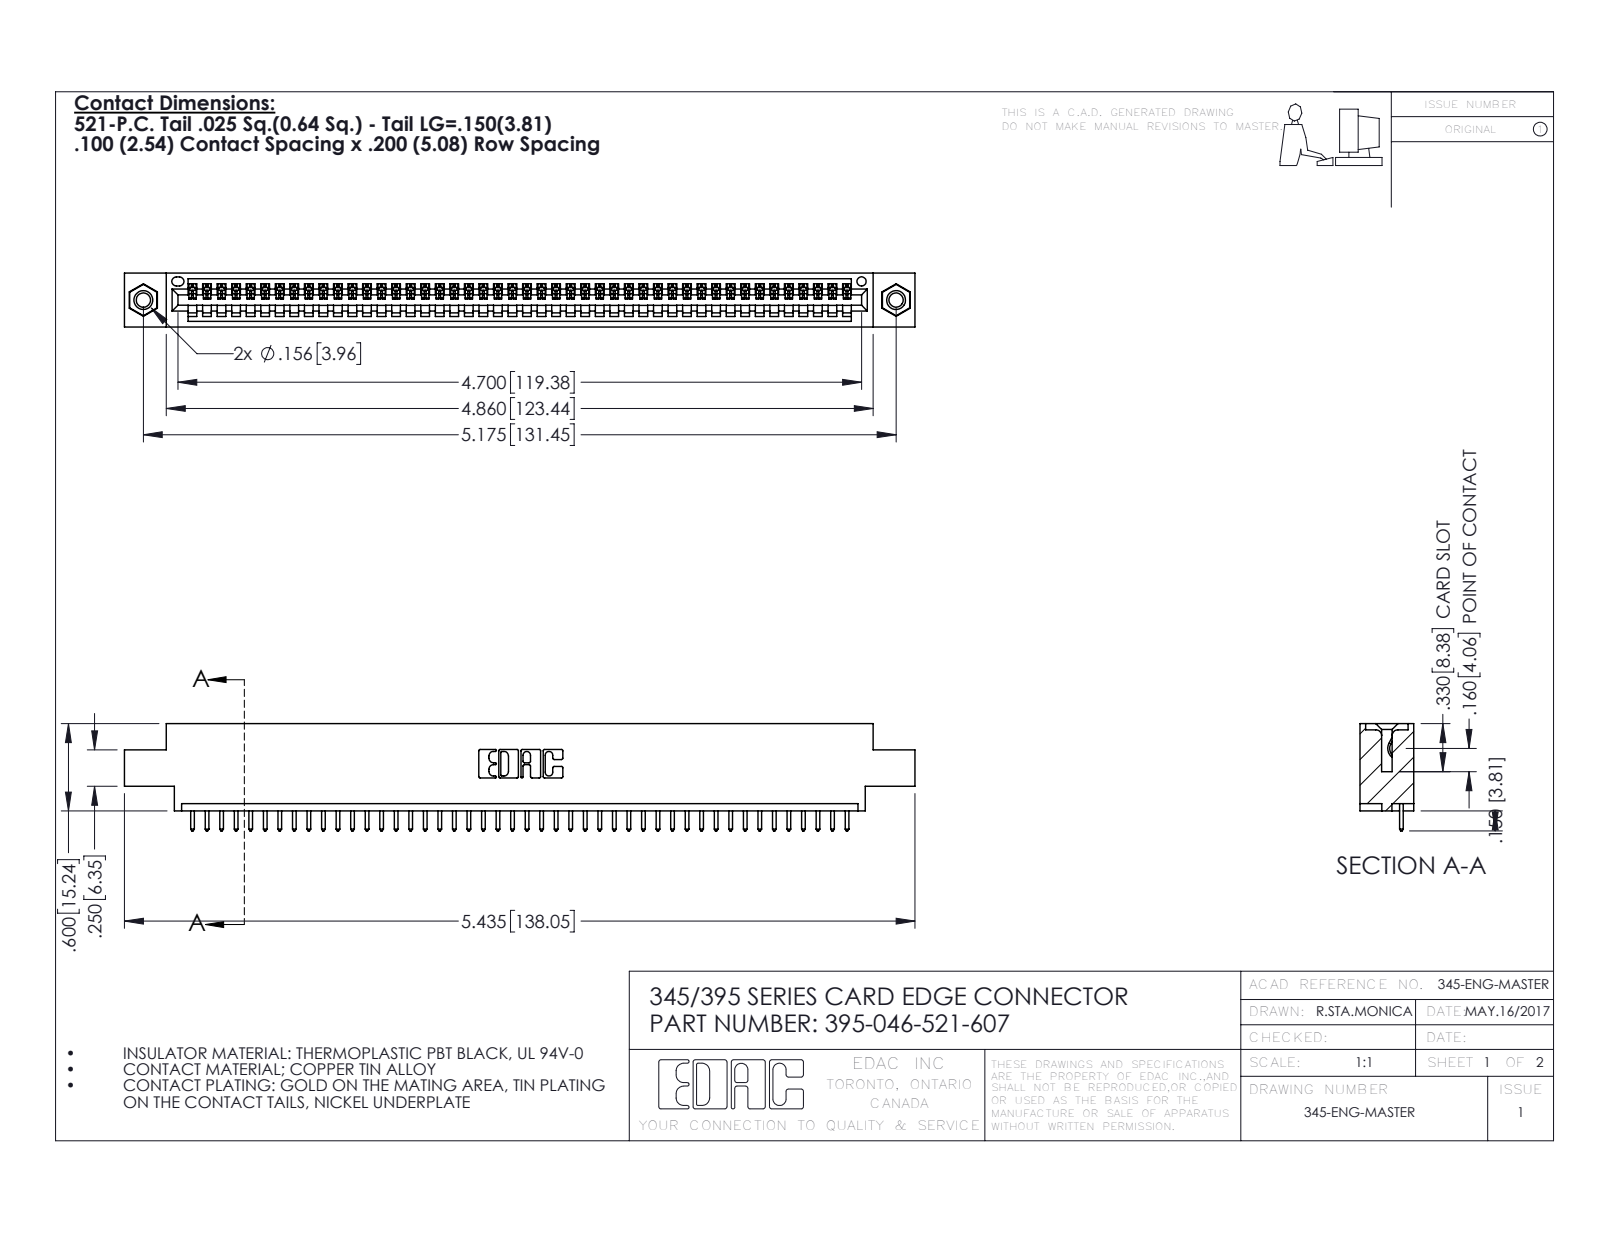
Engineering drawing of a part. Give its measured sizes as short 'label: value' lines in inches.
name: 345-250-001_345-250-005-103; 395-046-521-607; 345-292-001_345-293-121; 345 Part_0.170 Offset - 0.156 Dia-TI
written by: SolidWorks 2016 (CONFIG_CONTROL_DESIGN)
unit: in
bodies: 49 solids, 2858 faces (1956 planar, 886 cylindrical, 16 other)
size: 5.435 × 0.737 × 0.37
volume: 0.786 in³; area: 26.08 in²
holes: 2× ⌀0.098, 2× ⌀0.125, 2× ⌀0.156, 1× ⌀0.064
bosses: 2× ⌀0.155
rounds: 92× R0.006, 92× R0.01, 22× R0.01, 6× R0.007, 6× R0.031, 3× R0.026, 2× R0.031, 2× R0.04
face distances: 0.072, 0.298, 0.37, 0.2, 0.098, 0.272, 0.025, 0.225, 0.175, 0.149
hole spacings: 0.27, 4.939, 5.175
